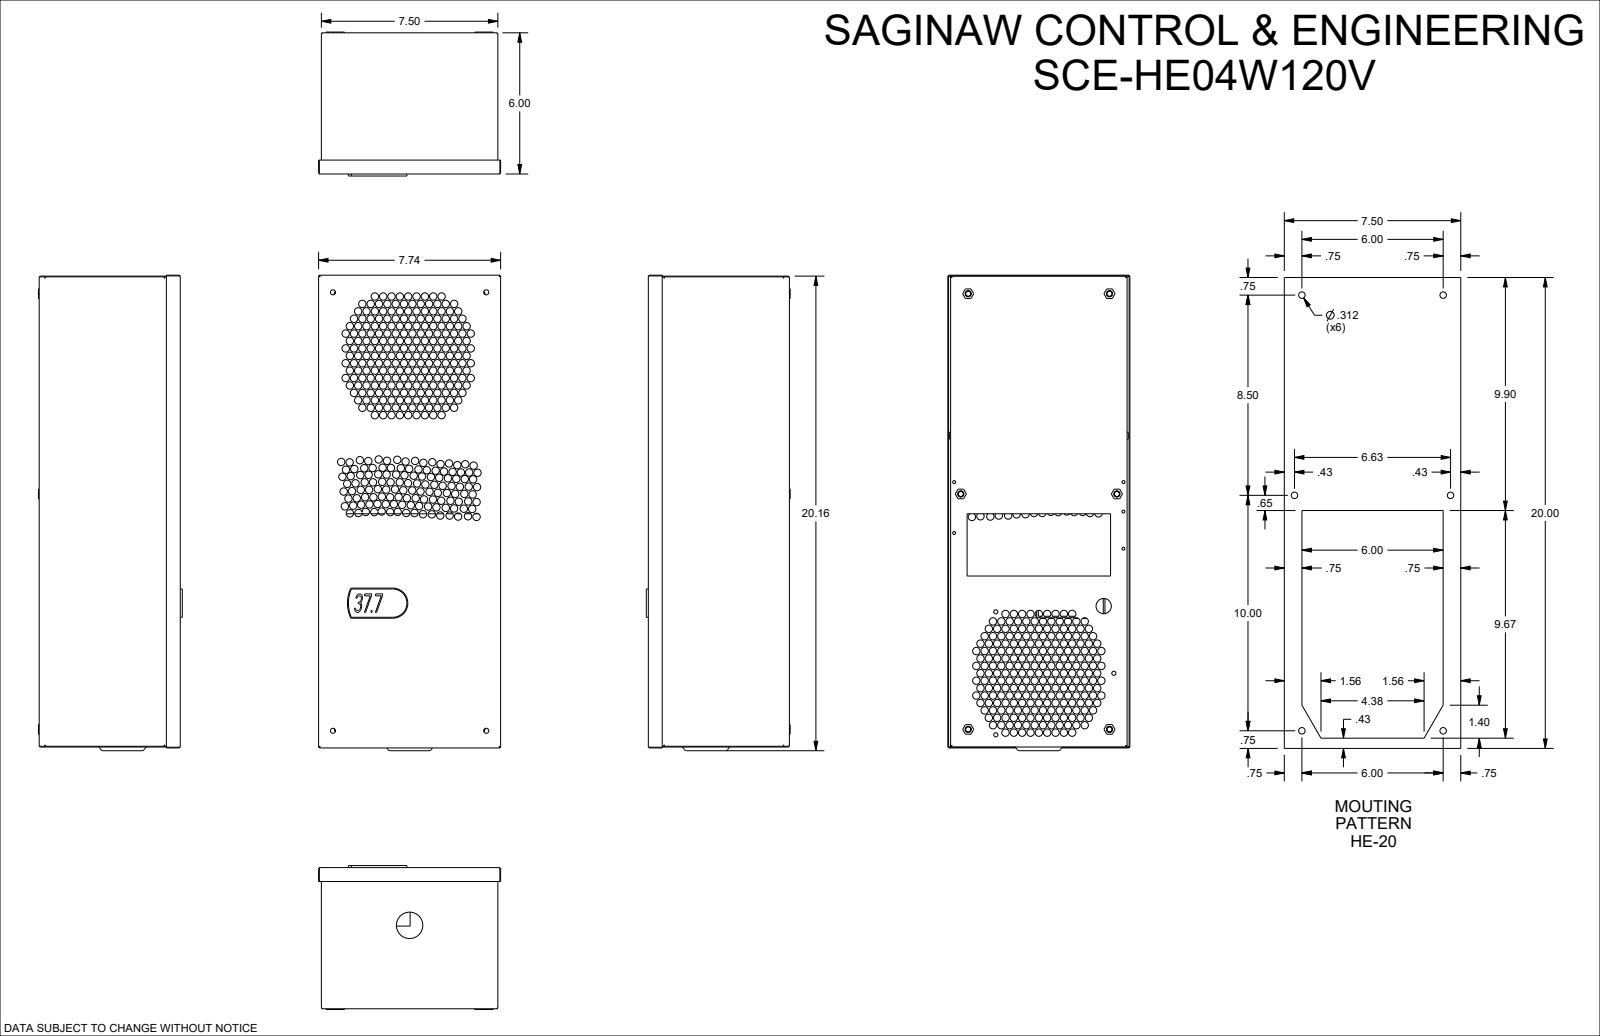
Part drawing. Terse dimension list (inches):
name: SCE-HE04W120V
written by: SolidWorks 2023 (AUTOMOTIVE_DESIGN)
unit: in
bodies: 1 solid, 1404 faces (765 planar, 636 cylindrical, 3 other)
size: 20.197 × 7.736 × 6.116
volume: 901.1 in³; area: 659.9 in²
holes: 598× ⌀0.315, 6× ⌀0.264, 5× ⌀0.126, 4× ⌀0.217, 3× ⌀0.177, 1× ⌀0.65, 1× ⌀1.122
rounds: 8× R0.063, 1× R0.6, 1× R0.64, 1× R1.477, 1× R1.517
face distances: 5.996, 7.5, 0.031, 5.965, 20, 5.933, 0.118, 7.618, 7.736, 0.039
hole spacings: 0.354, 0.709, 1.063, 1.309, 1.417, 1.772, 2.126, 2.48
